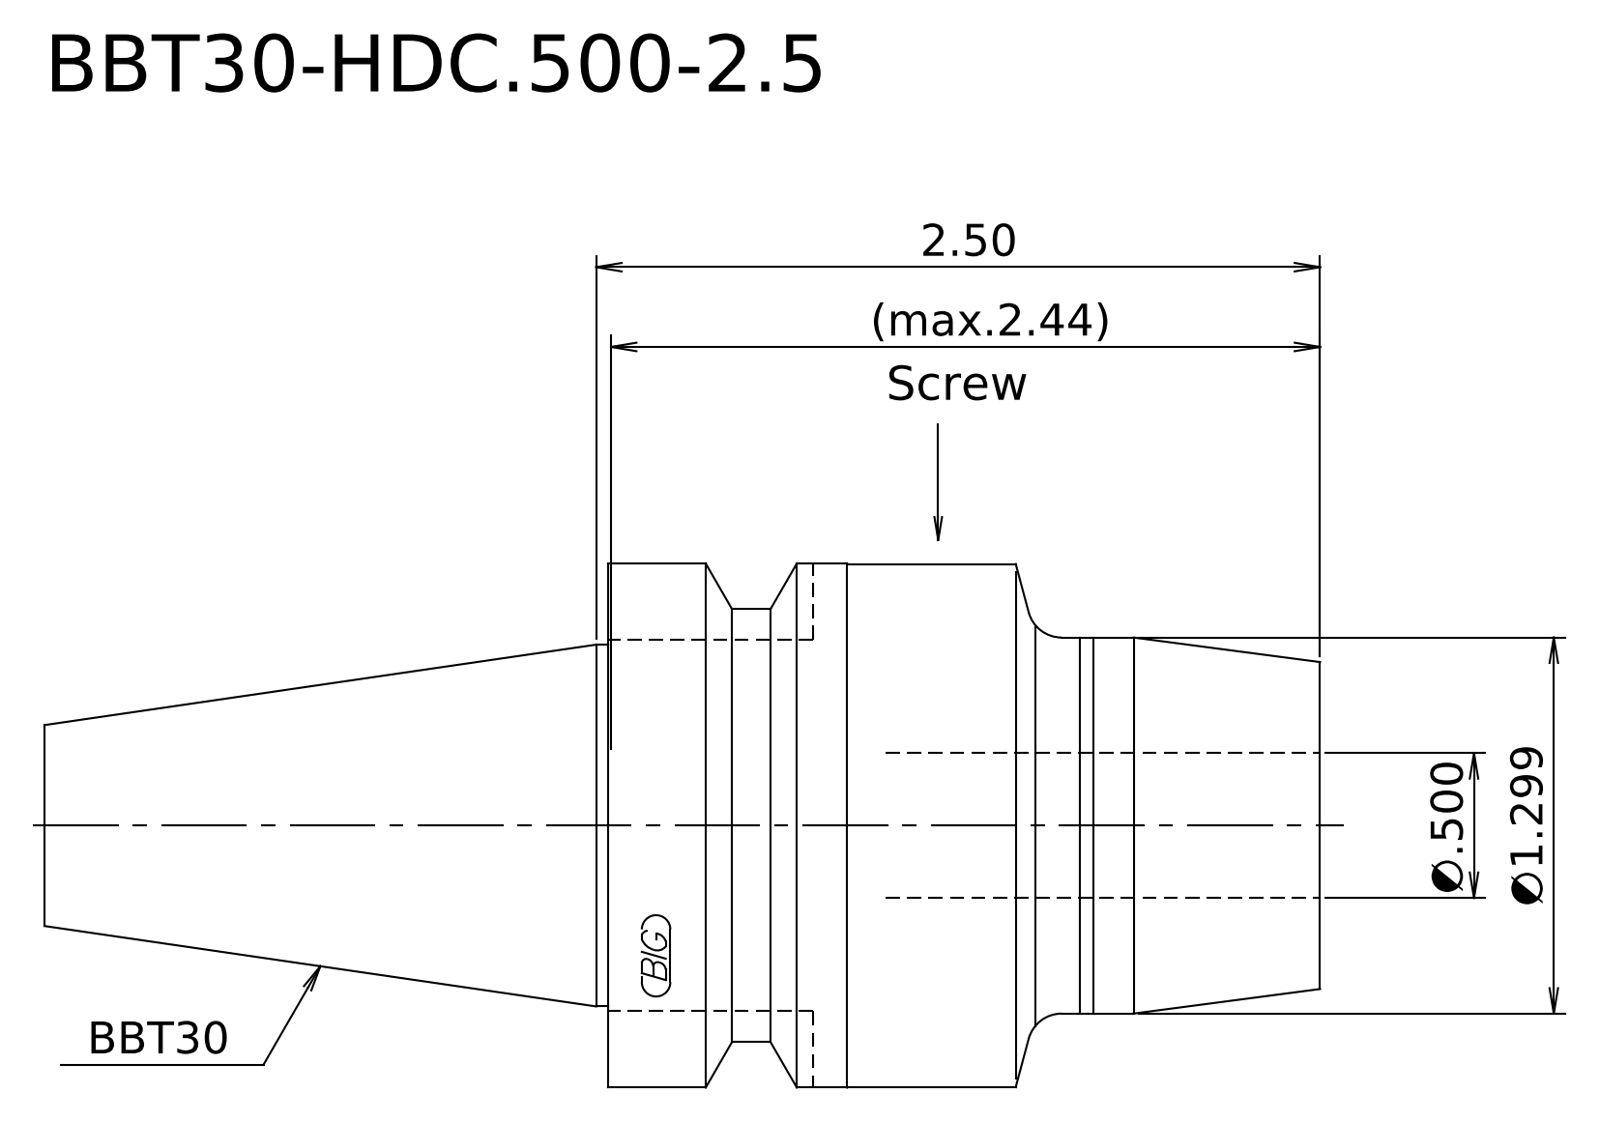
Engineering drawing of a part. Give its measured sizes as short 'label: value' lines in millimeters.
written by: Kubotek KeyCreator 2011 V10.0.2 (22737) (automotive_design)
unit: mm
bodies: 1 solid, 16 faces (3 planar, 6 cylindrical, 7 other)
size: 111.9 × 46 × 46
volume: 102 964 mm³; area: 14 523 mm²
bosses: 1× ⌀46, 1× ⌀45.9, 1× ⌀38, 1× ⌀33, 1× ⌀31.75
face distances: 62.5, 111.9, 49.4
